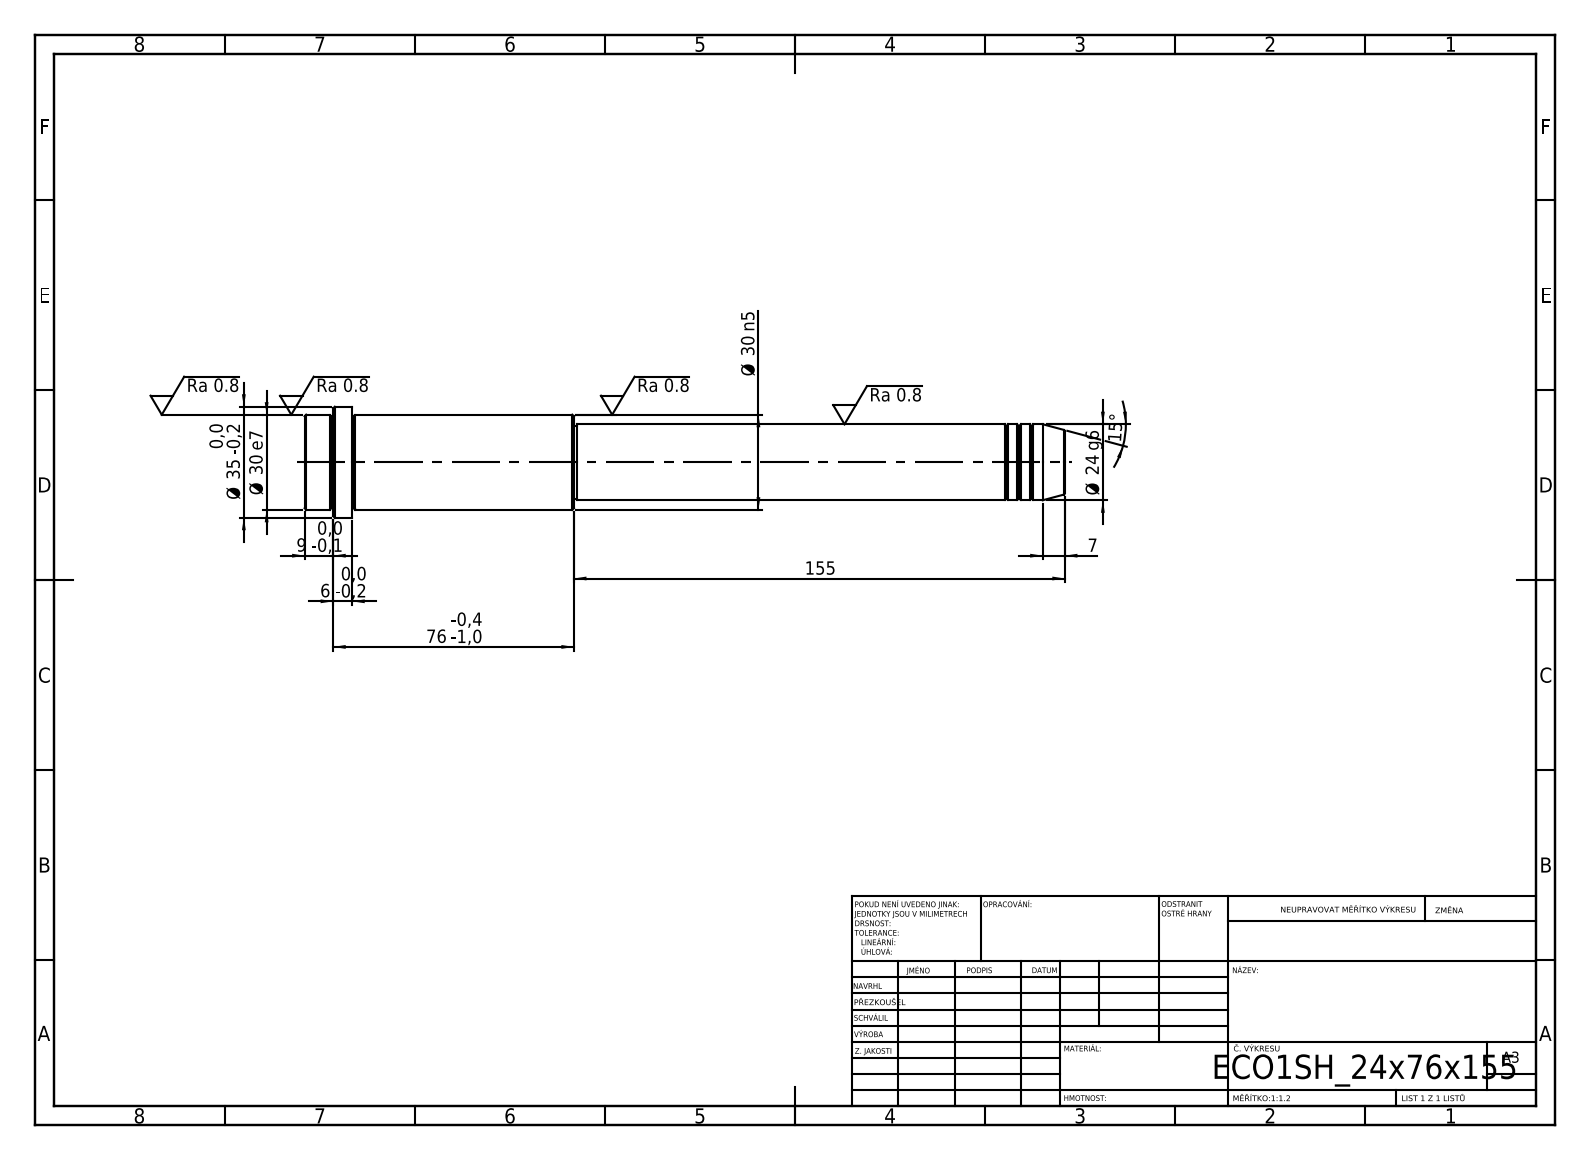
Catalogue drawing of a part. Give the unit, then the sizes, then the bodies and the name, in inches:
Units: inches
Overall size (bounding box): 9.449 × 1.378 × 1.378
Round bosses / shafts (diameter × count): ⌀1.378 ×1, ⌀1.181 ×1, ⌀0.945 ×1, ⌀0.906 ×1
Main face-to-face distances: 9.449, 8.858, 0.591, 6.102, 2.756, 3.346, 9.094, 2.992, 0.236, 0.354
Volume: 7.996 in³ · Surface area: 33.72 in²
Bodies: 1 solid, 52 faces (6 planar, 16 cylindrical, 30 other)
STEP written by: SolidWorks 2019 (CONFIG_CONTROL_DESIGN)
